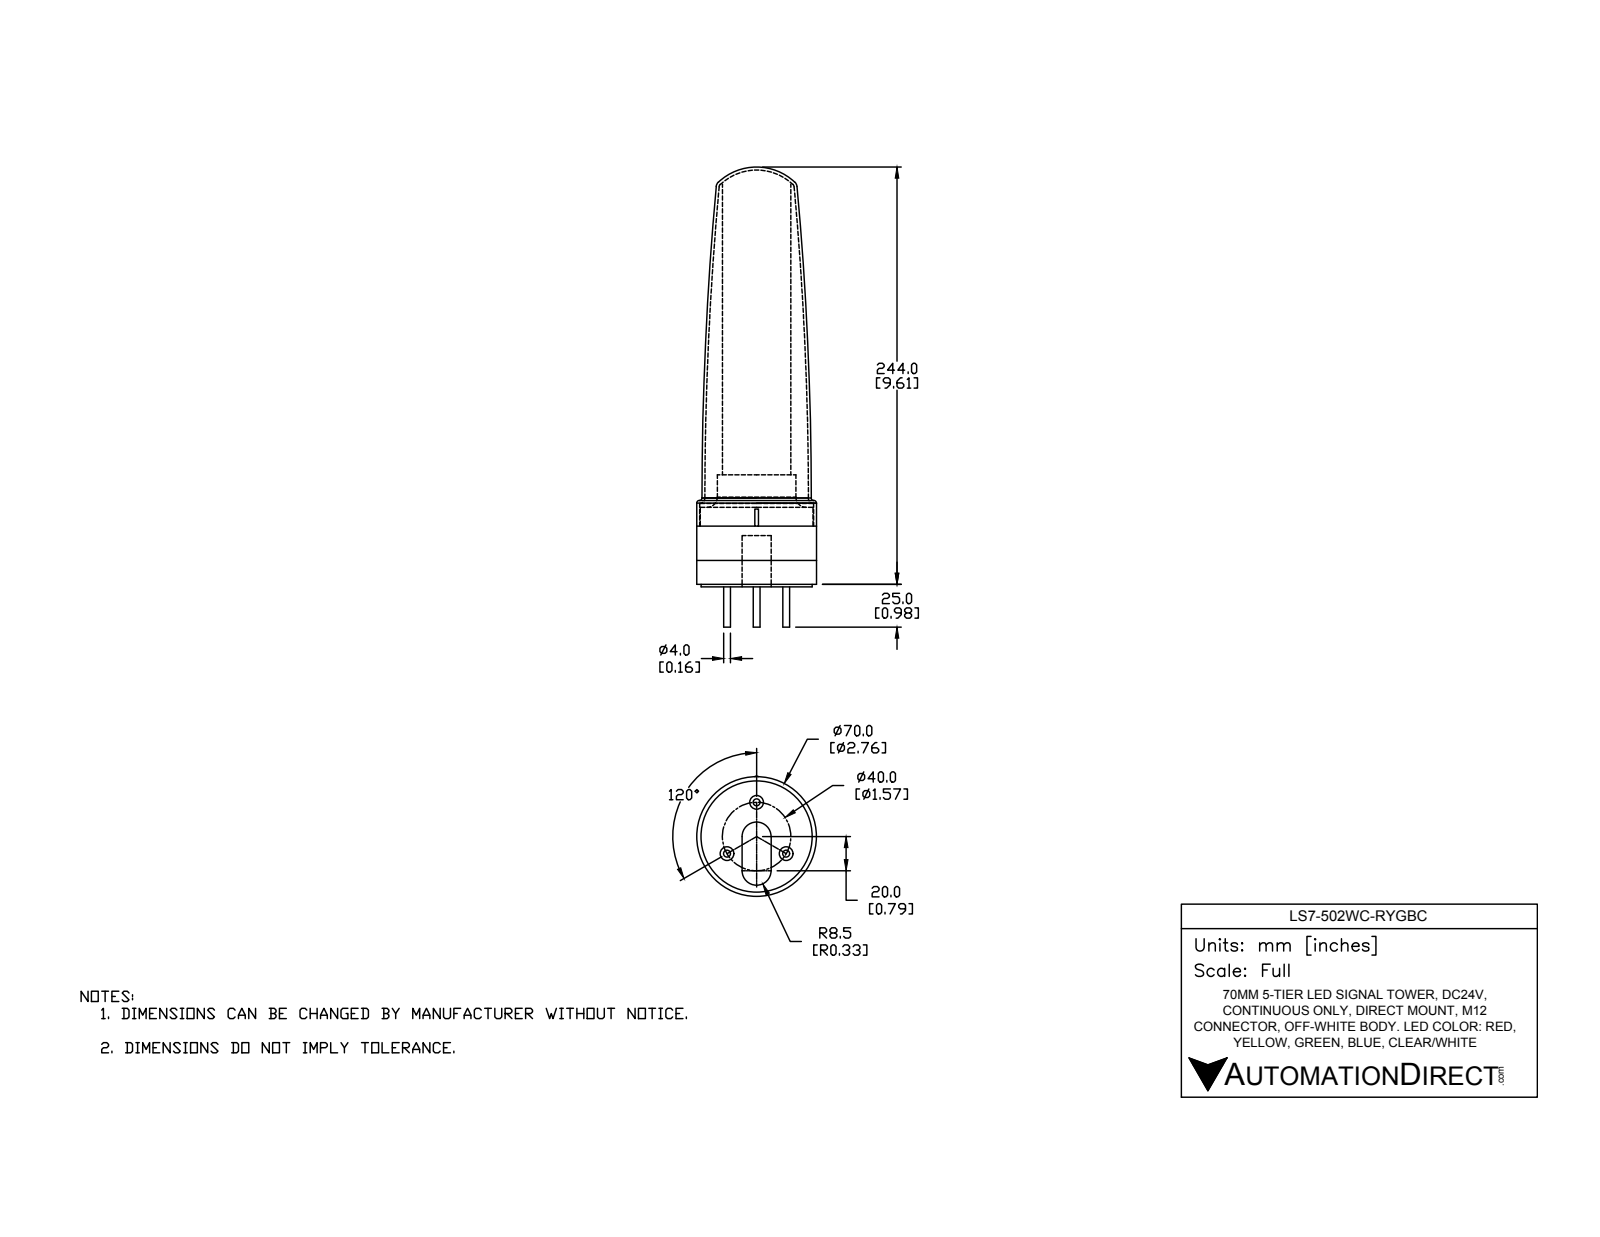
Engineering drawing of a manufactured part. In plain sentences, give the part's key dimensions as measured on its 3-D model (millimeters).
The part is named "LS7-502WC-RYGBC". Its 3-D file was written by "SolidWorks 2016 (AUTOMOTIVE_DESIGN)". It is 8 solids with 84 faces: 27 planar, 39 cylindrical and 18 other. Overall it measures 269 by 70.3 by 70 millimeters. Its volume is 468 745 cubic millimeters and its surface area 136 804 square millimeters. Round holes: 3 of diameter 8, 1 of diameter 66.6. Round bosses or shafts: 3 of diameter 4, 1 of diameter 70, 1 of diameter 66, 1 of diameter 65, 1 of diameter 46, 1 of diameter 40. Partial cylindrical surfaces (rounded edges, fillets, slot ends): 2 of radius 8.5, 1 of radius 1, 1 of radius 2. The main face-to-face distances are 14, 64, 50, 15.5, 1.5, 65.5, 30, 35.5, 235.5, 234. The hole center spacings are 20, 34.64.
